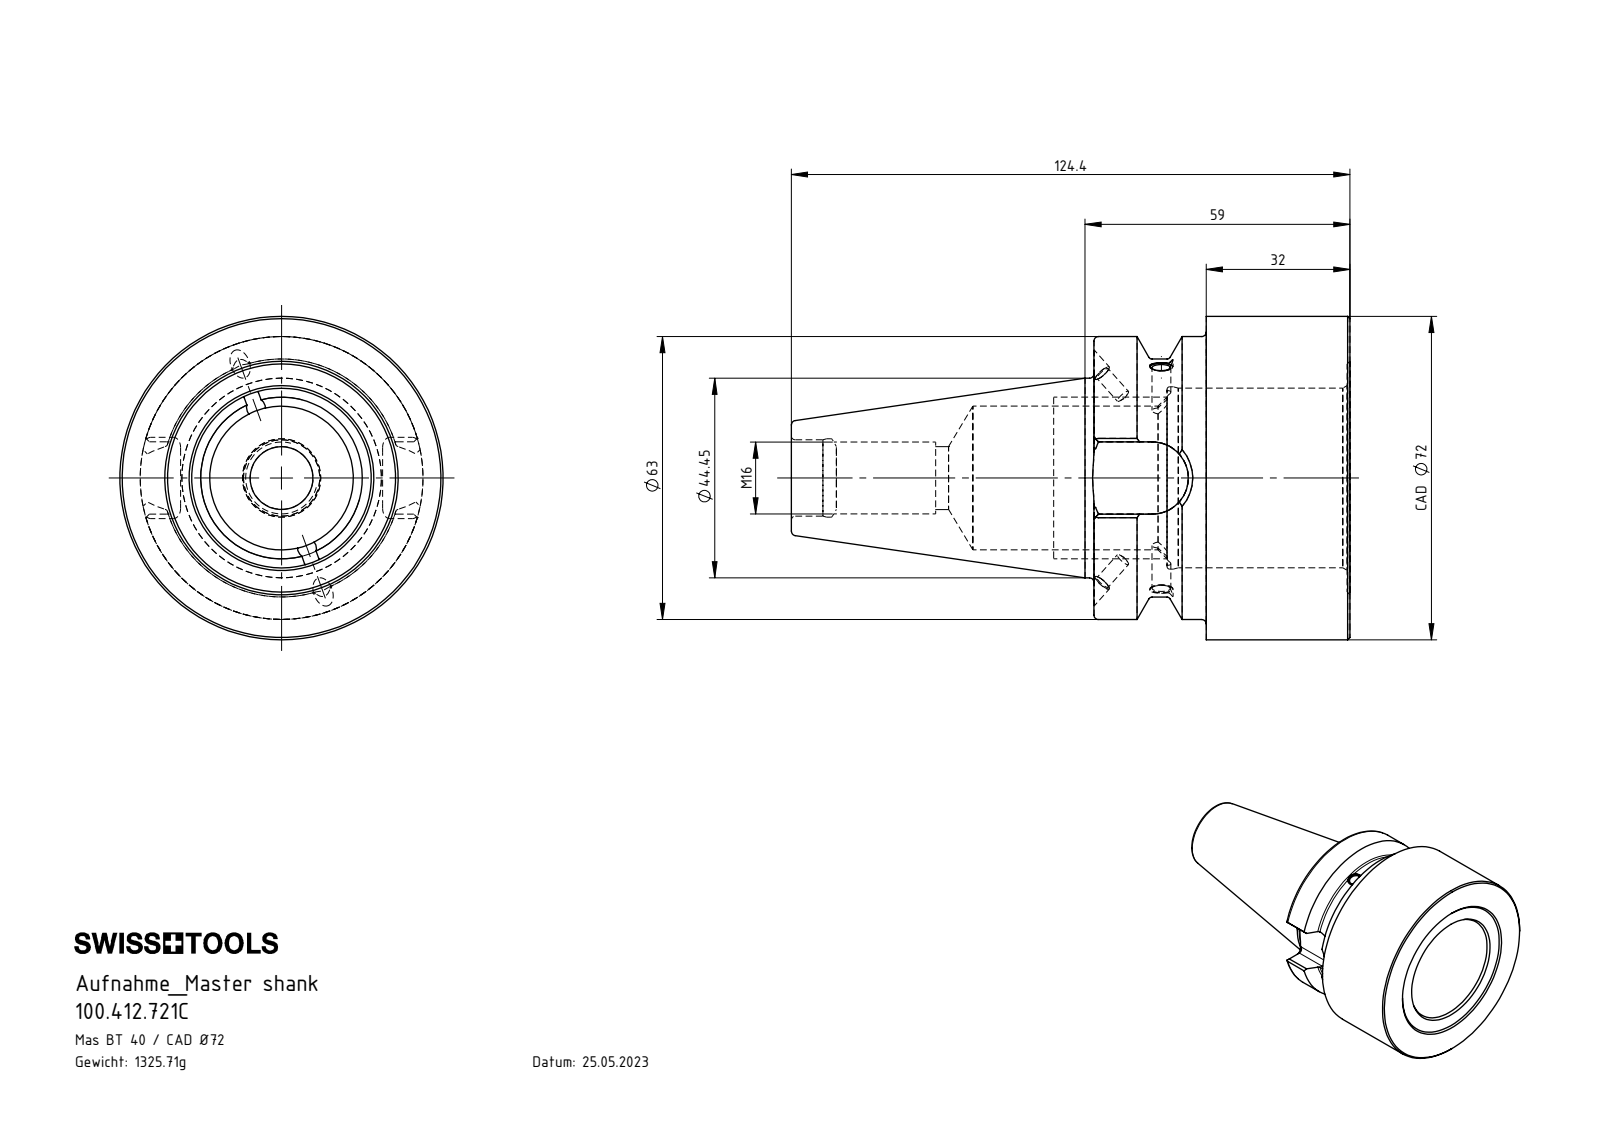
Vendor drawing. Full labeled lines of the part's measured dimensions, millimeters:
Part name (STEP PRODUCT): BB4-CA7.K01.059_A; ISO 4026 - M5 x 5_PreviewCfg; ISO 4026 - M4 x 4; 100.412.721C
STEP written by: SolidWorks 2022 (CONFIG_CONTROL_DESIGN)
Units: millimetres
Bodies: 4 solids, 183 faces (49 planar, 57 cylindrical, 77 other)
Overall size (bounding box): 124.4 × 72 × 72
Volume: 169 087 mm³ · Surface area: 38 780 mm²
Round holes (diameter × count): ⌀4.2 ×4, ⌀3.3 ×2, ⌀5.2 ×2, ⌀14 ×1, ⌀17 ×1, ⌀17.45 ×1, ⌀32 ×1, ⌀40 ×1, ⌀40.6 ×1
Round bosses / shafts (diameter × count): ⌀5 ×2, ⌀72 ×1, ⌀63 ×1, ⌀44.45 ×1, ⌀4 ×1
Partial cylindrical surfaces — rounded edges, fillets, slot ends (radius × count): R1.6 ×8, R8.05 ×1, R26.5 ×1
Main face-to-face distances: 57, 25, 32, 56.4, 31.4, 0.6, 45, 16.25, 8.75, 40.15
